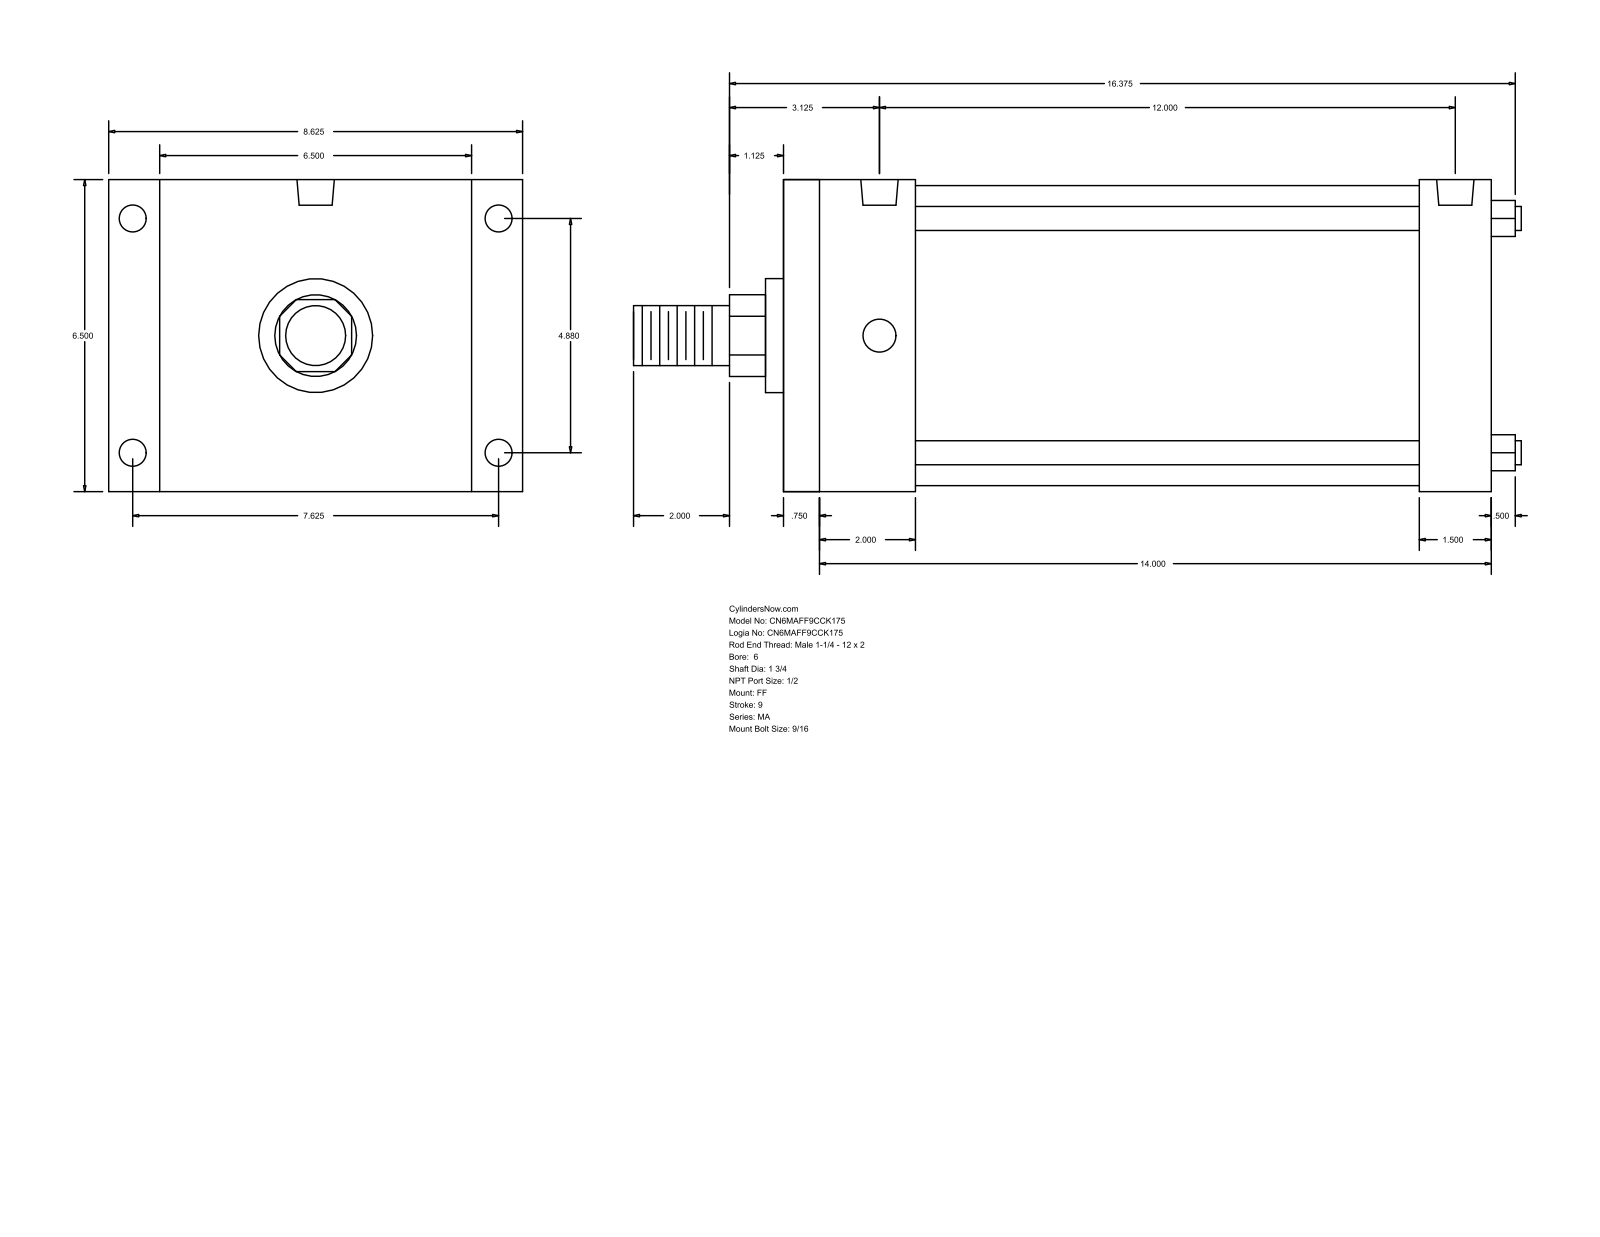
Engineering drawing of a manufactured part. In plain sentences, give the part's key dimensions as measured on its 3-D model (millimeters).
The part is named "MA_FF__0600_1.75". Its 3-D file was written by "GSSL Pune (CONFIG_CONTROL_DESIGN)". It is 0 solids with 92 faces: 64 planar, 28 cylindrical and 0 other. Overall it measures 469.9 by 219.07 by 165.1 millimeters. Round holes: 4 of diameter 14.29, 4 of diameter 17.46, 2 of diameter 19.77. Round bosses or shafts: 4 of diameter 12.7, 1 of diameter 158.75, 1 of diameter 60.33, 1 of diameter 44.45, 1 of diameter 31.75. Partial cylindrical surfaces (rounded edges, fillets, slot ends): 1 of radius 21.63. The main face-to-face distances are 165.1, 374.66, 19.05, 355.61, 69.85, 50.8, 304.81, 336.55, 317.5, 266.7. The hole center spacings are 123.96, 193.68, 229.95, 304.8.
